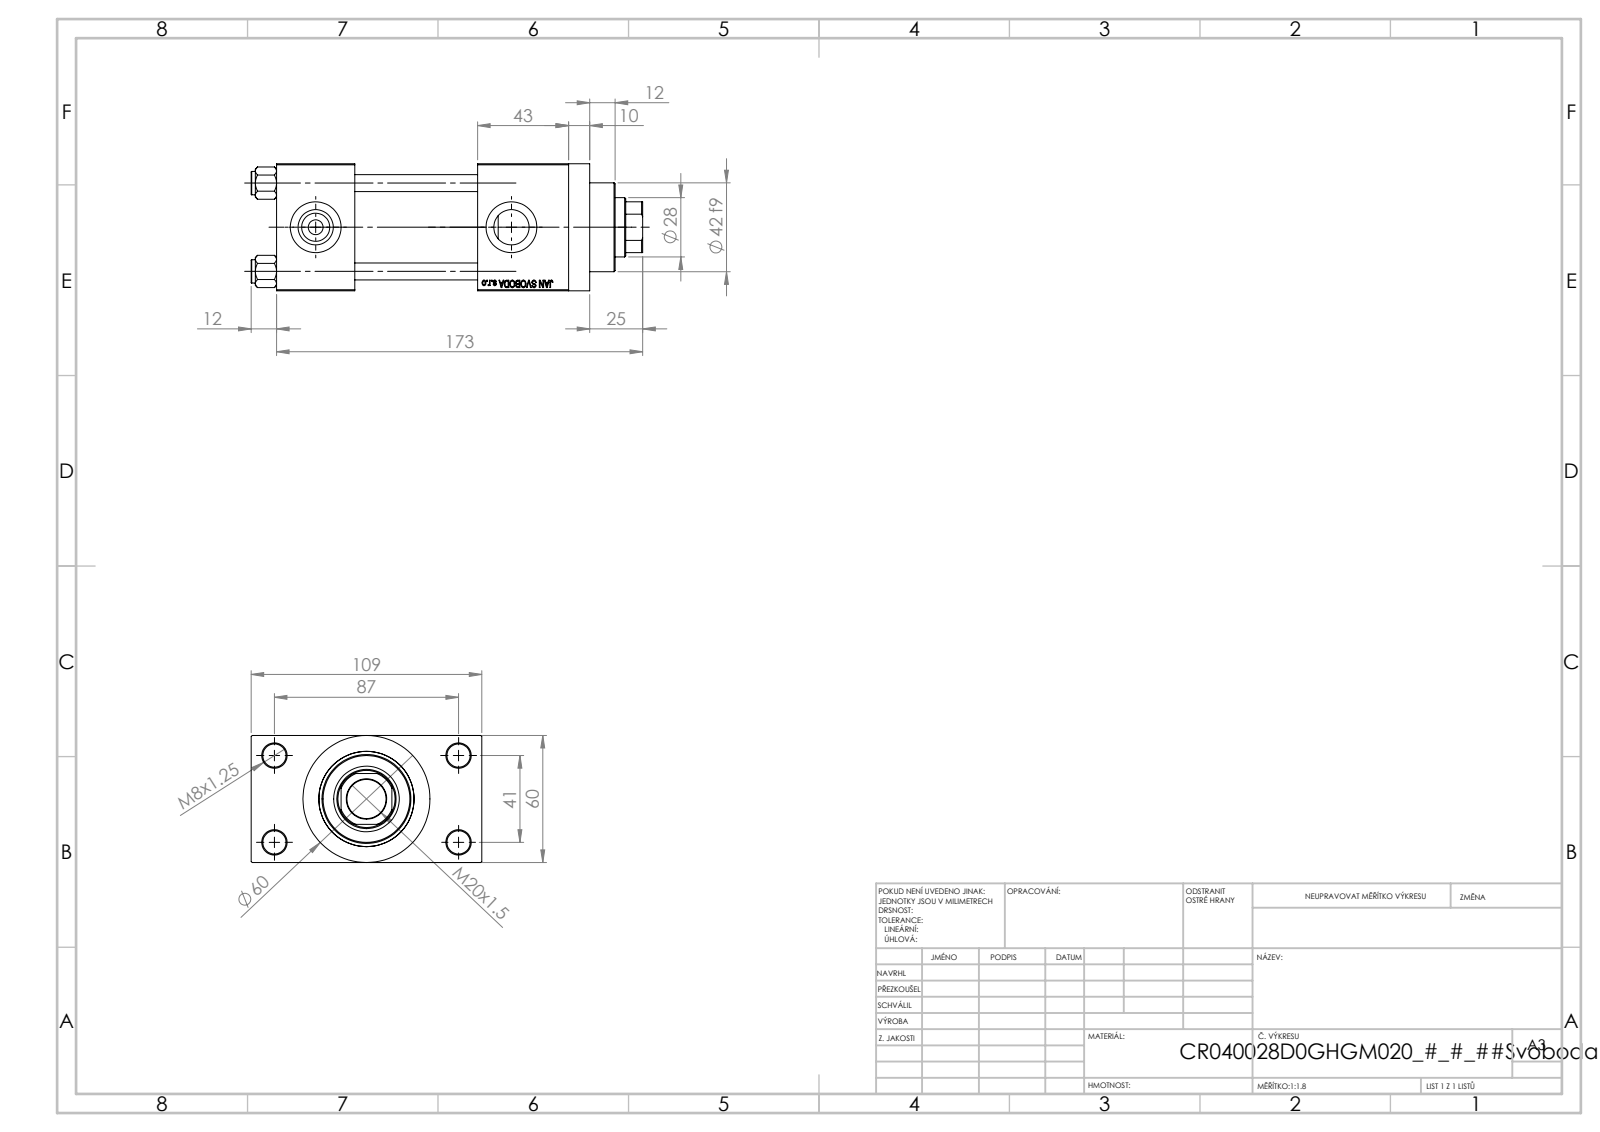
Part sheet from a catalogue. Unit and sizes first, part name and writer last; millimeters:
Units: millimetres
Overall size (bounding box): 185 × 109 × 60
Round holes (diameter × count): ⌀8 ×4, ⌀11 ×4, ⌀7 ×2, ⌀16.66 ×2, ⌀24 ×2, ⌀18.5 ×1, ⌀28 ×1, ⌀31 ×1, ⌀40 ×1, ⌀45 ×1
Round bosses / shafts (diameter × count): ⌀11 ×4, ⌀60 ×1, ⌀46 ×1, ⌀42 ×1
Partial cylindrical surfaces — rounded edges, fillets, slot ends (radius × count): R13.5 ×1
Main face-to-face distances: 60, 58, 24.5, 84.5, 37, 95, 138, 101, 43, 109
Hole centre spacings: 22.65, 29.49, 41.7, 47.15, 48.09, 64.35, 76.49, 41
Volume: 528 877 mm³ · Surface area: 129 106 mm²
Bodies: 11 solids, 1104 faces (498 planar, 88 cylindrical, 518 other)
Part name (STEP PRODUCT): V215CR_D_TYCINKA; V215_VC_A; V215CR_VCP_D; V215CR_D_Body (+1 more)
STEP written by: SolidWorks 2019 (CONFIG_CONTROL_DESIGN)
